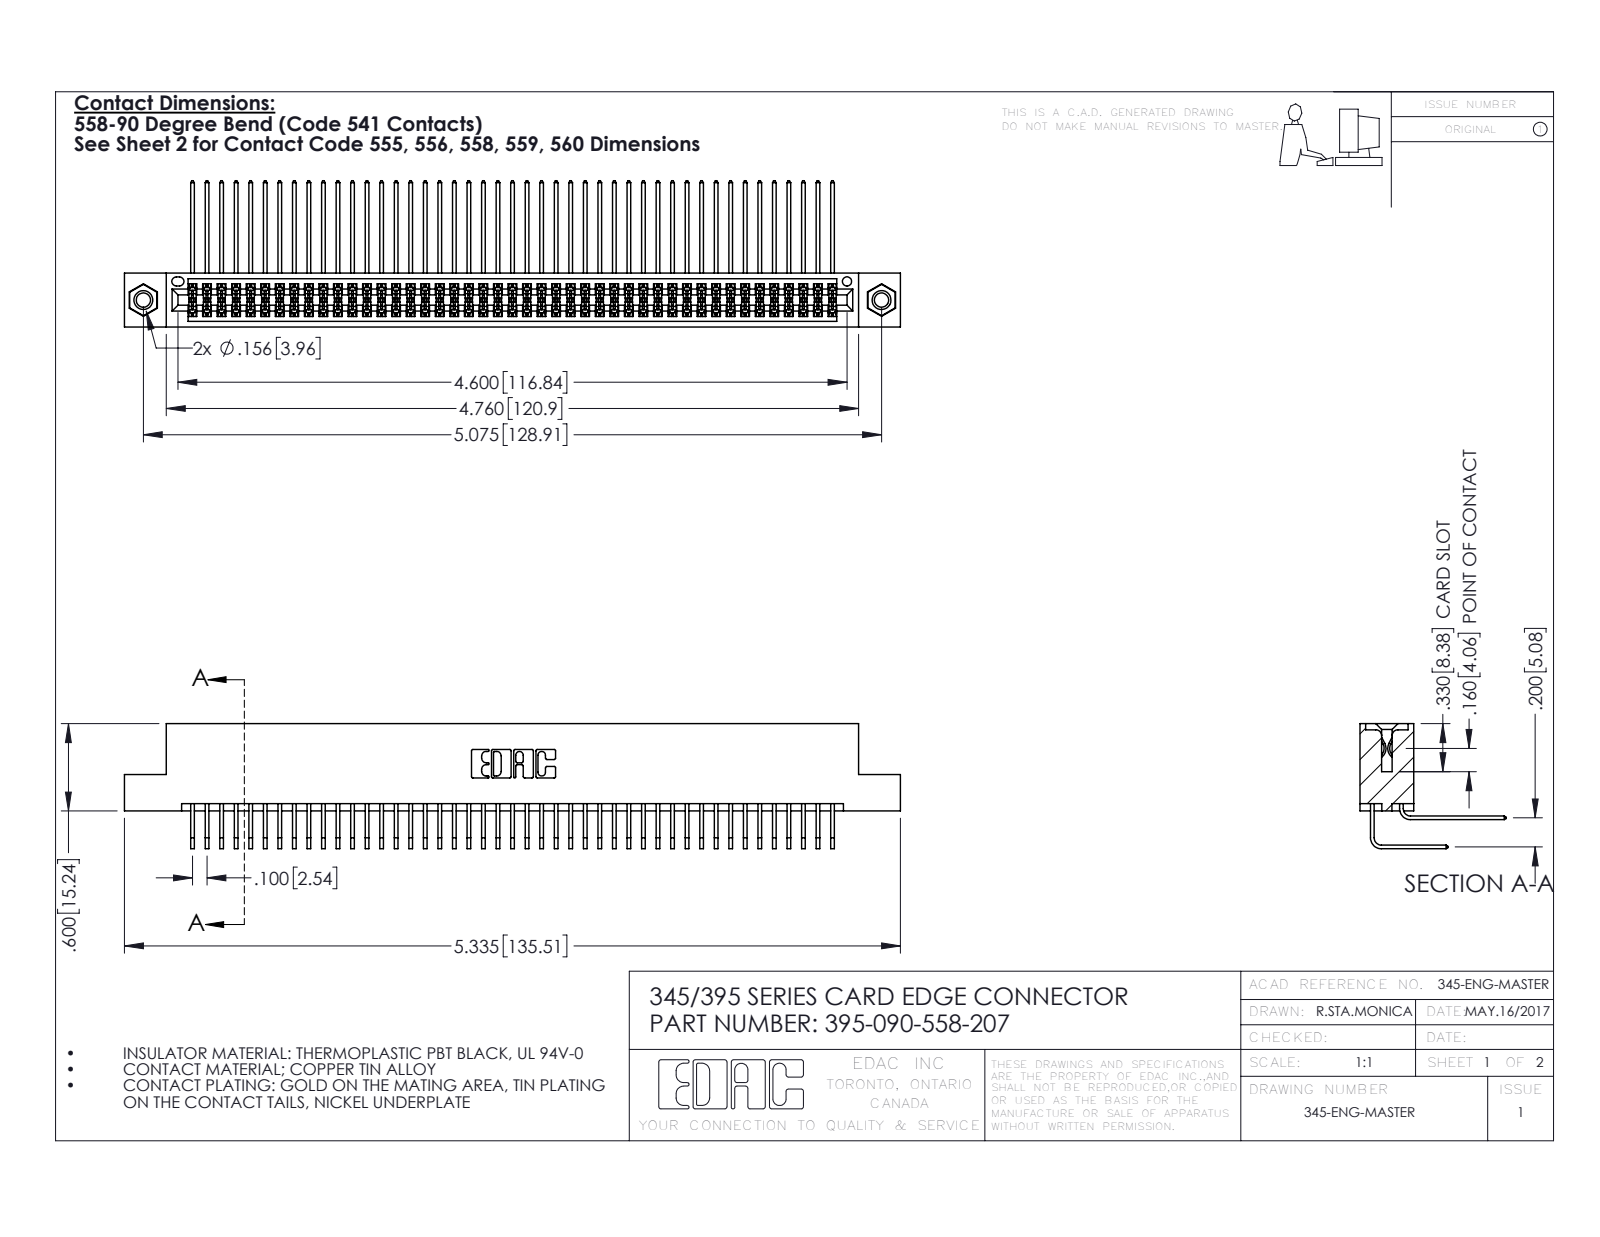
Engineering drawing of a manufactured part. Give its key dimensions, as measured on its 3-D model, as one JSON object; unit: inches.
{"part_name": "395-090-558-207; 345-292-001_558 Tail - 2; 345-250-001_345-250-005-103; 345 Part_Flush Mounting Lugs - 0.156 Dia-TI (+1 more)", "step_written_by": "SolidWorks 2016 (CONFIG_CONTROL_DESIGN)", "units": "inches", "bodies": {"solids": 93, "faces": 4866, "planar": 3262, "cylindrical": 1588, "other": 16}, "overall_size": [5.335, 1.005, 0.859], "volume_in3": 0.836, "surface_area_in2": 35.3, "round_holes": [[0.098, 2], [0.125, 2], [0.156, 2], [0.064, 1]], "round_bosses_or_shafts": [[0.155, 2]], "partial_cylinders_radius": [[0.006, 136], [0.01, 22], [0.007, 6], [0.031, 6], [0.026, 3], [0.014, 2], [0.019, 2], [0.022, 2]], "face_to_face_distances": [0.072, 0.298, 0.2, 0.37, 0.098, 0.272, 0.025, 0.225, 0.025, 0.175], "hole_center_spacings": [0.27, 4.839, 5.075]}
